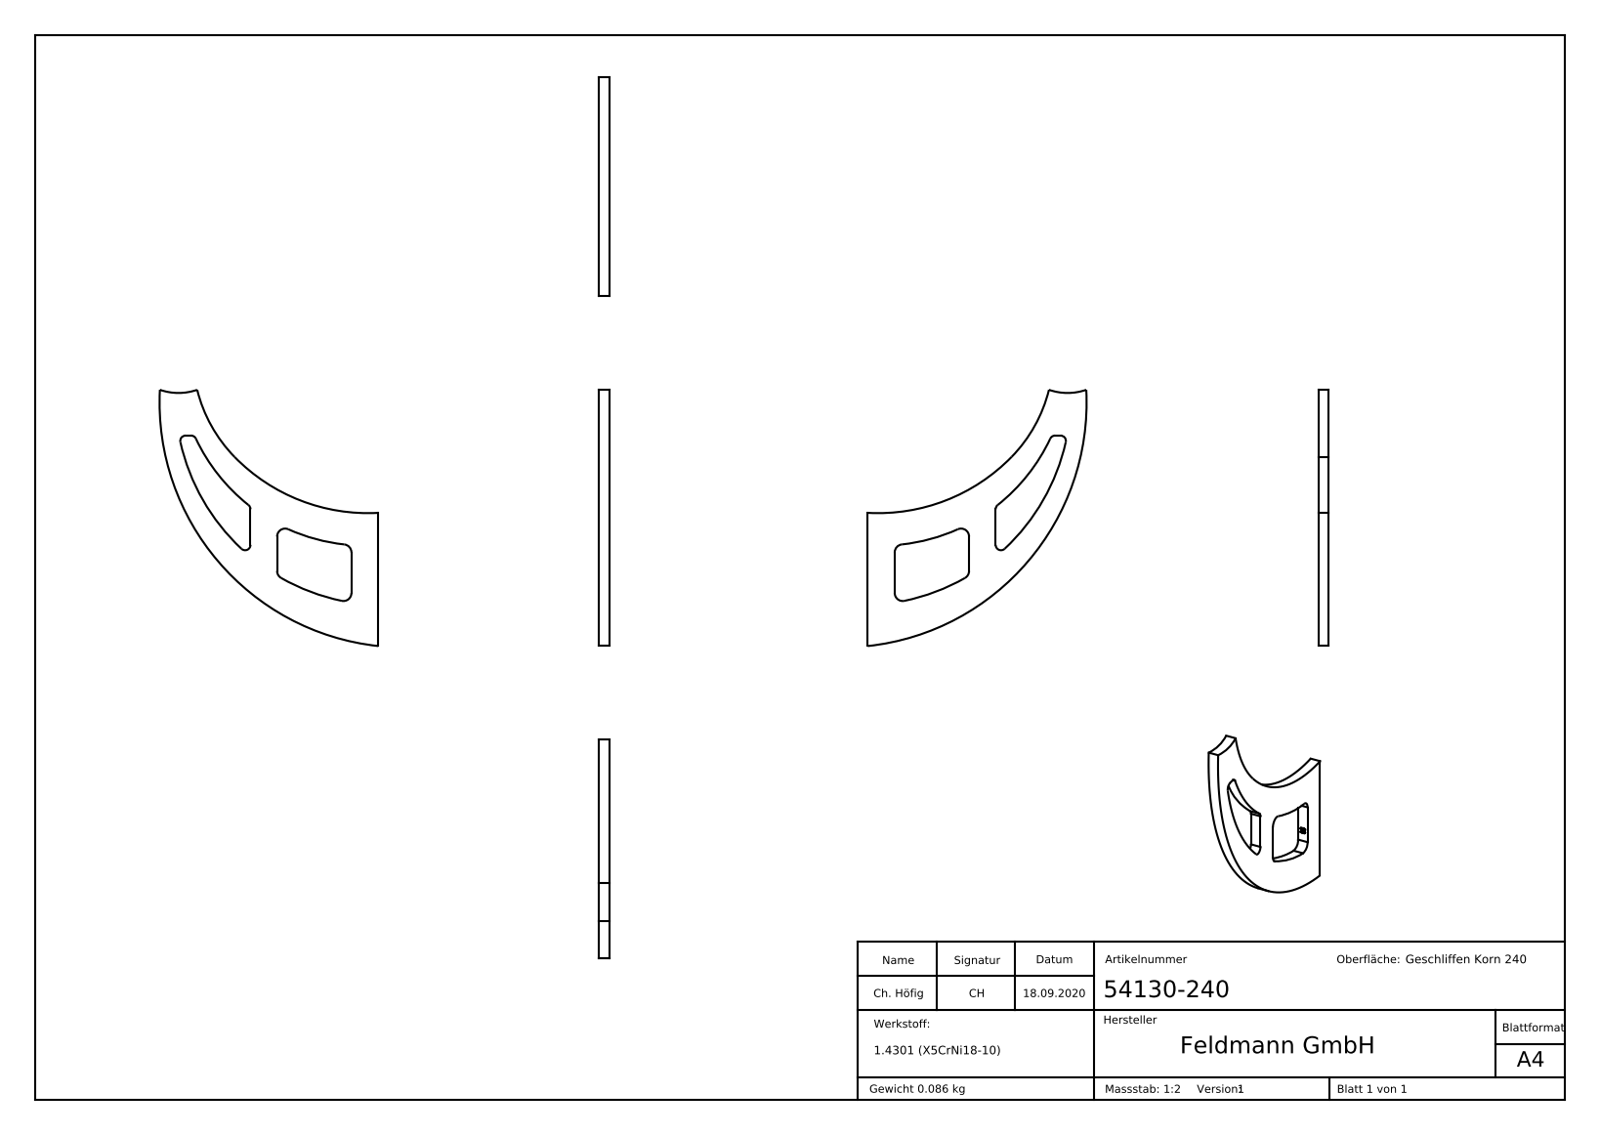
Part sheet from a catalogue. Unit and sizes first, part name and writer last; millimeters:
Units: millimetres
Overall size (bounding box): 96.19 × 82.12 × 4
Partial cylindrical surfaces — rounded edges, fillets, slot ends (radius × count): R2 ×4, R3 ×4, R70 ×2, R21.2 ×1, R55 ×1, R78.5 ×1, R92 ×1
Main face-to-face distances: 4, 10.1, 48, 37.9, 10, 38, 27.9, 28, 1.14, 1.46
Volume: 10 933 mm³ · Surface area: 7 439 mm²
Bodies: 1 solid, 246 faces (136 planar, 16 cylindrical, 94 other)
Part name (STEP PRODUCT): 54130-240
STEP written by: SolidWorks 2018 (CONFIG_CONTROL_DESIGN)
